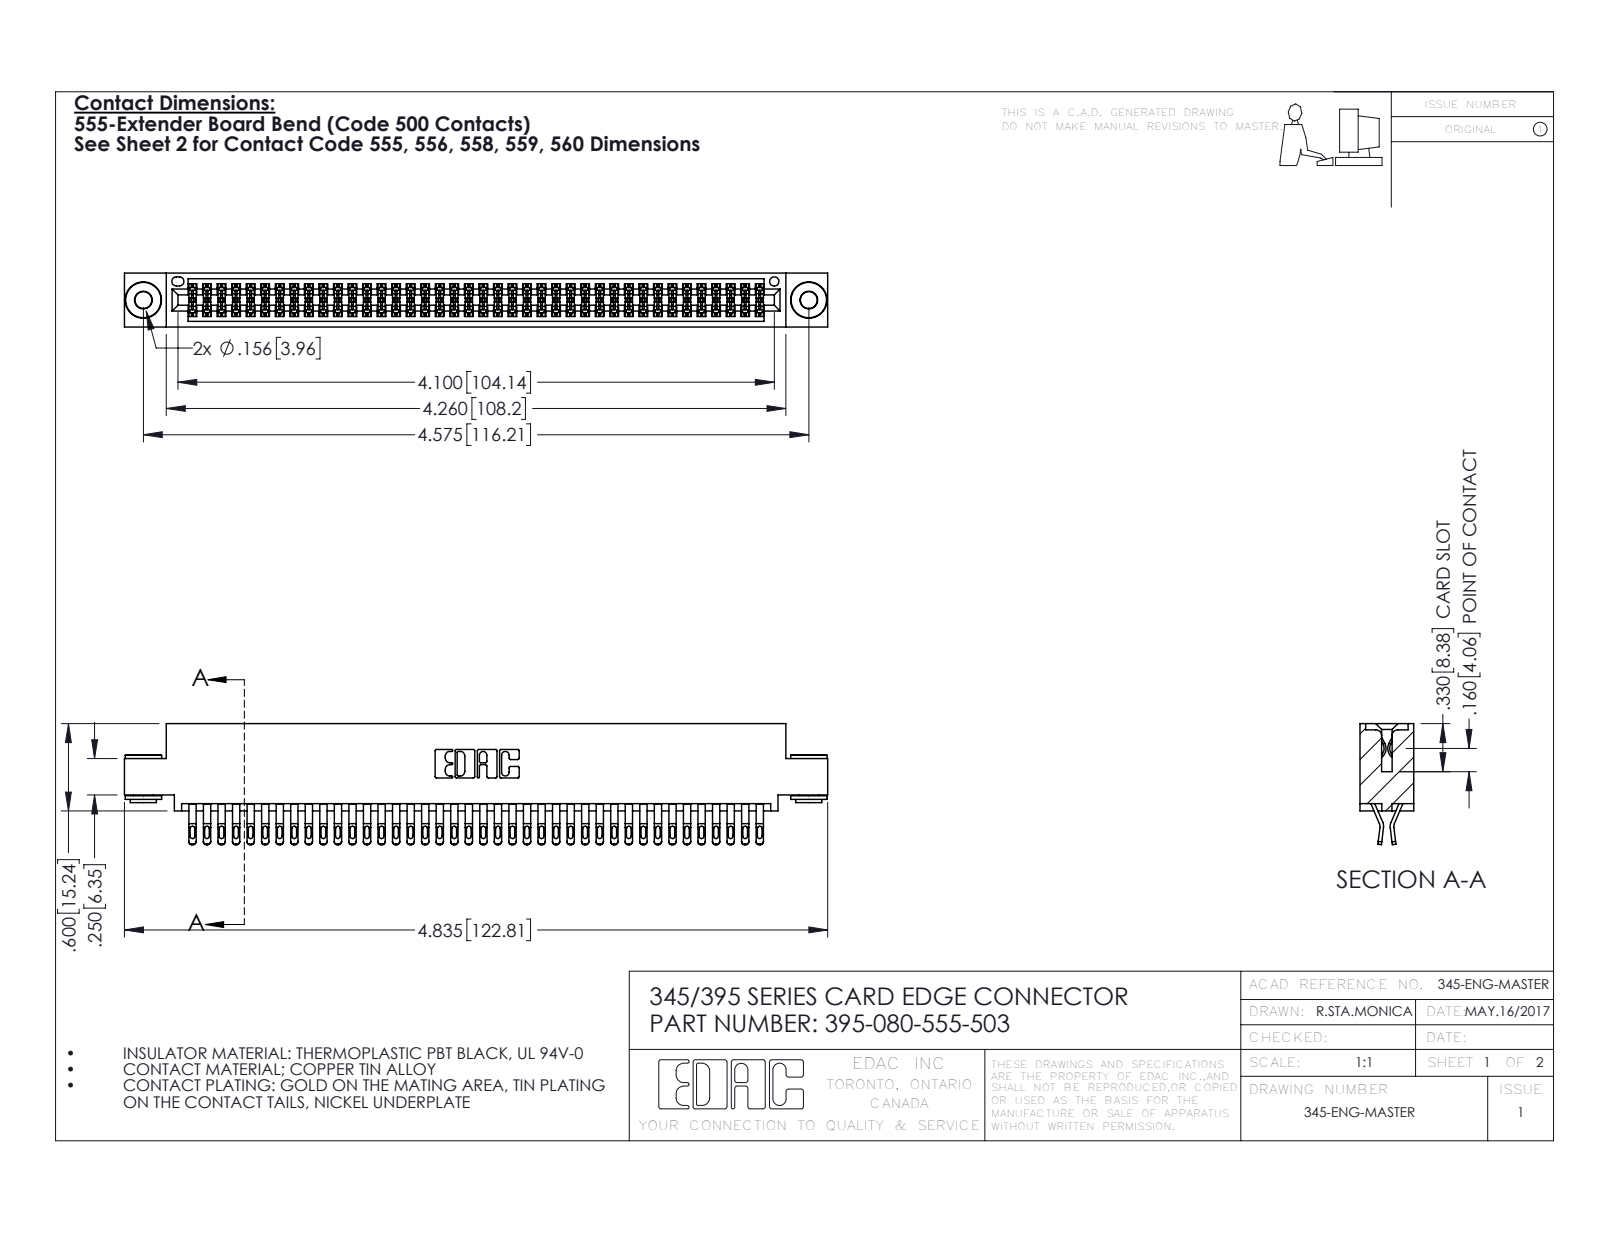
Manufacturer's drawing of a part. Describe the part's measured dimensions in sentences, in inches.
The part is named "395-080-555-503; 345 Part_0.110 Offset - 0.156 Dia-TH; 345-250-002_345-250-002-102; 345-292-001_555 Tail". Its 3-D file was written by "SolidWorks 2016 (CONFIG_CONTROL_DESIGN)". It is 83 solids with 4648 faces: 2574 planar, 2066 cylindrical and 8 other. Overall it measures 4.835 by 0.832 by 0.37 inches. Its volume is 0.738 cubic inches and its surface area 29.35 square inches. Round holes: 2 of diameter 0.116, 2 of diameter 0.156, 1 of diameter 0.064. Round bosses or shafts: 2 of diameter 0.25, 2 of diameter 0.18, 2 of diameter 0.136. Partial cylindrical surfaces (rounded edges, fillets, slot ends): 200 of radius 0.016, 160 of radius 0.02, 120 of radius 0.006, 22 of radius 0.01, 6 of radius 0.007, 6 of radius 0.031, 3 of radius 0.026, 2 of radius 0.01. The main face-to-face distances are 0.072, 0.298, 0.025, 0.37, 0.2, 0.098, 0.272, 0.225, 0.175, 0.149. The hole center spacings are 0.27, 4.339, 4.575.
